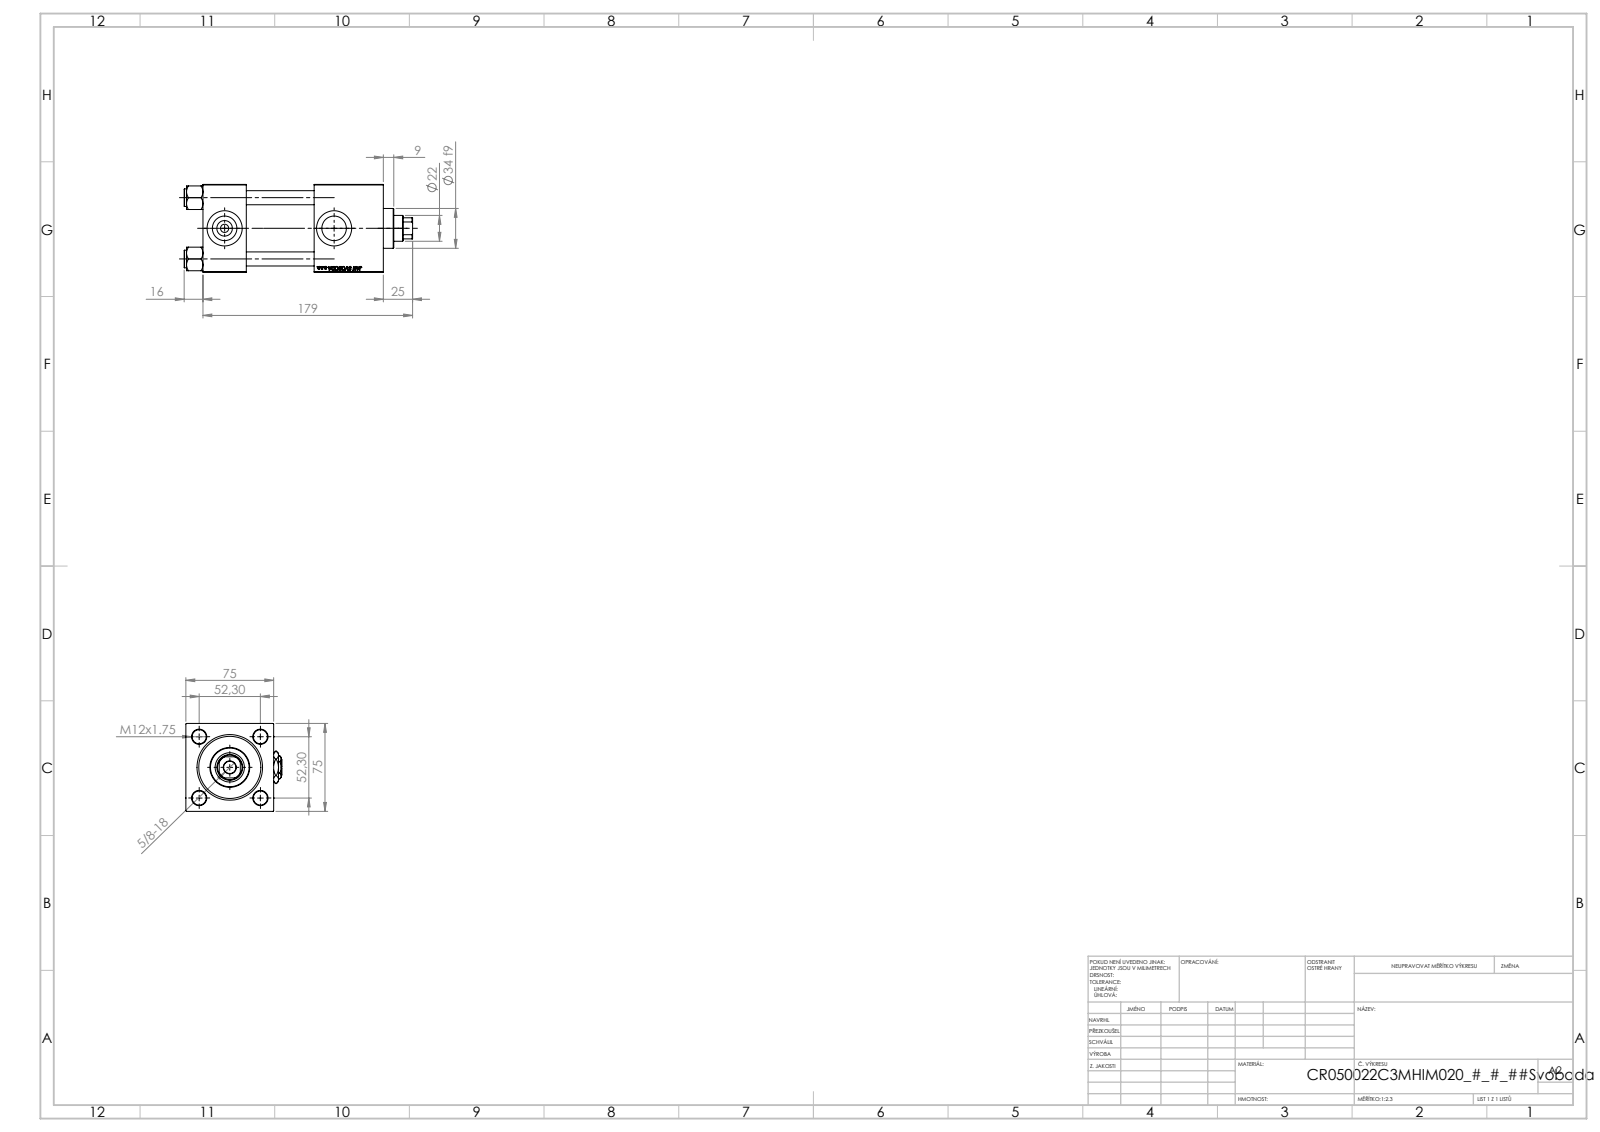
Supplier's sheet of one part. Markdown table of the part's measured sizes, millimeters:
| quantity | value |
| --- | --- |
| part name | V215CR_C_TYCINKA; V215CR_VCP_C; V215_VC_A; Zatka_pro_OIL_PORT (+2 more) |
| STEP written by | SolidWorks 2019 (CONFIG_CONTROL_DESIGN) |
| units | millimeters |
| bodies | 13 solids, 1249 faces (573 planar, 98 cylindrical, 578 other) |
| overall size | 195 × 82.27 × 75 |
| volume | 651 837 mm³ |
| surface area | 151 762 mm² |
| round holes (diameter × count) | 12 × 4, 7 × 2, 20.96 × 2, 30 × 2, 10.5 × 1, 22 × 1, 25 × 1, 41 × 1, 50 × 1, 53 × 1 |
| round bosses / shafts (diameter × count) | 15 × 4, 56 × 1, 34 × 1 |
| partial cylindrical surfaces (radius × count) | 10.5 × 1 |
| main face-to-face distances | 75, 37, 154, 117, 95, 58, 59, 125.3, 88.3, 30.3 |
| hole center spacings | 36.98, 52.3, 73.96, 93.5 |
